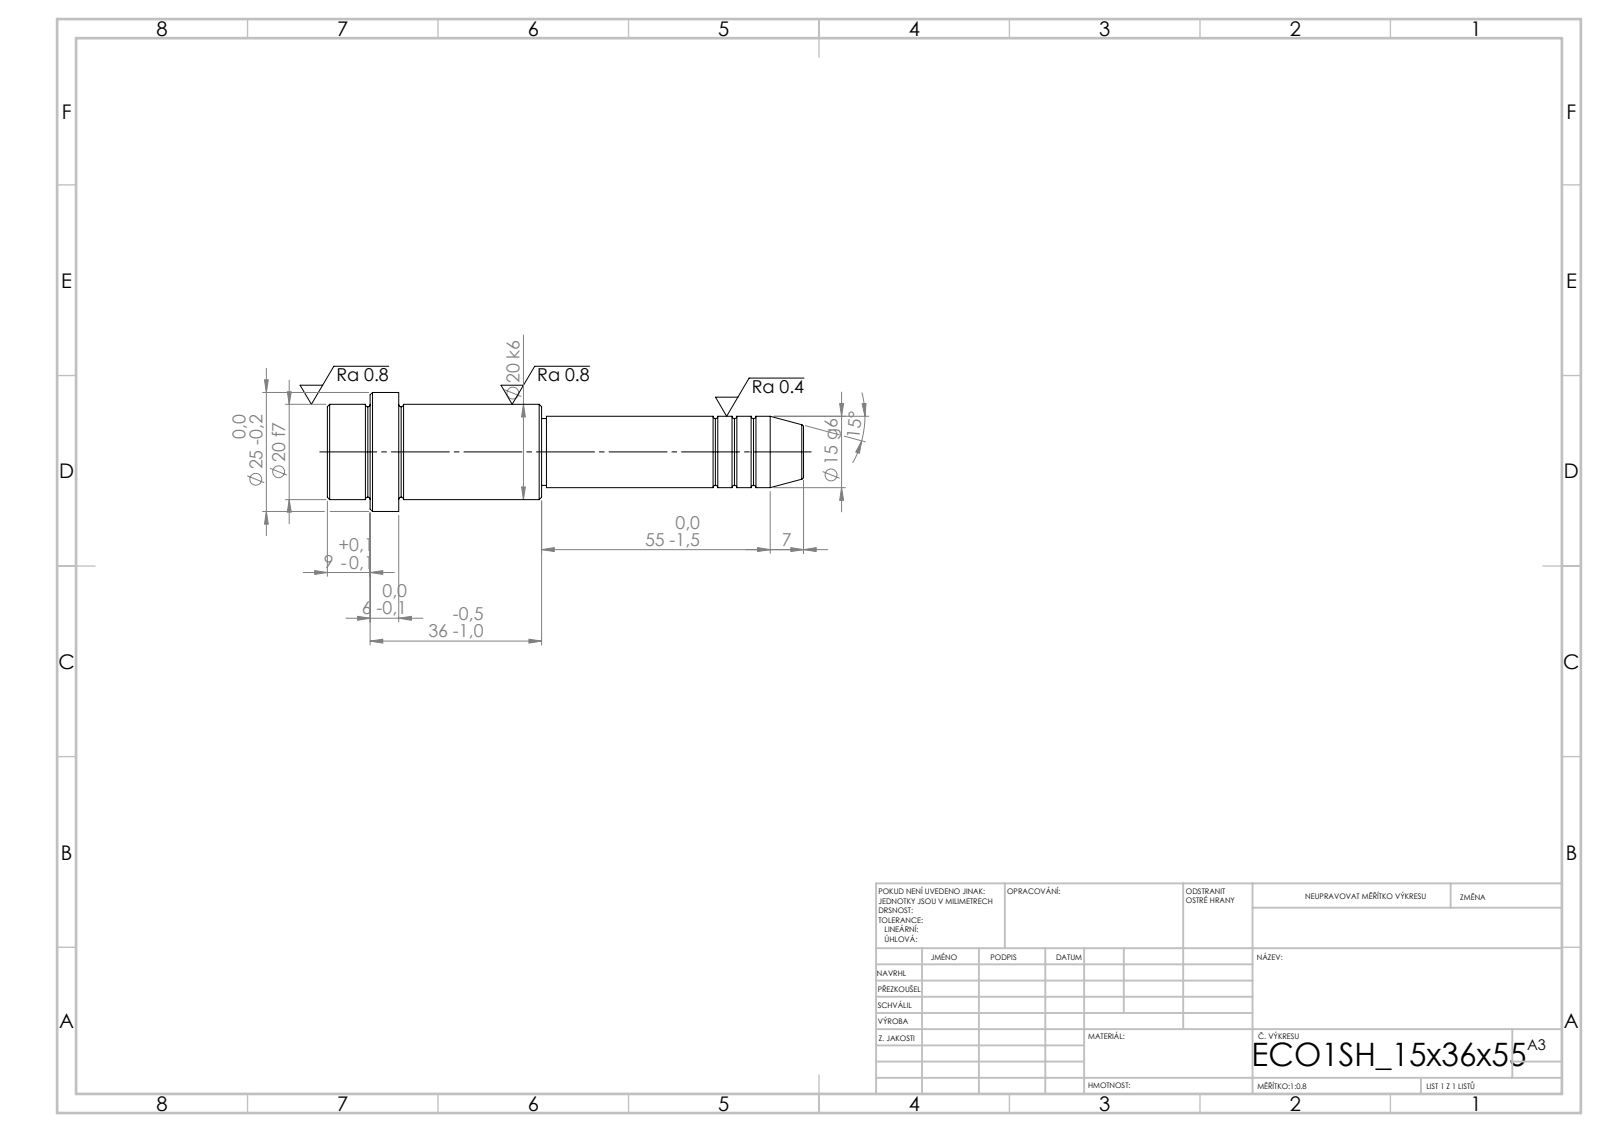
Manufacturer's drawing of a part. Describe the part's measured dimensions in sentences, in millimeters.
Its 3-D file was written by "SolidWorks 2019 (CONFIG_CONTROL_DESIGN)". It is 1 solid with 52 faces: 6 planar, 16 cylindrical and 30 other. Overall it measures 100 by 25 by 25 millimeters. Its volume is 24 482 cubic millimeters and its surface area 6 501 square millimeters. Round bosses or shafts: 1 of diameter 25, 1 of diameter 20, 1 of diameter 15, 1 of diameter 14. The main face-to-face distances are 15, 6, 9, 30, 36, 45, 55, 85, 91, 100.
